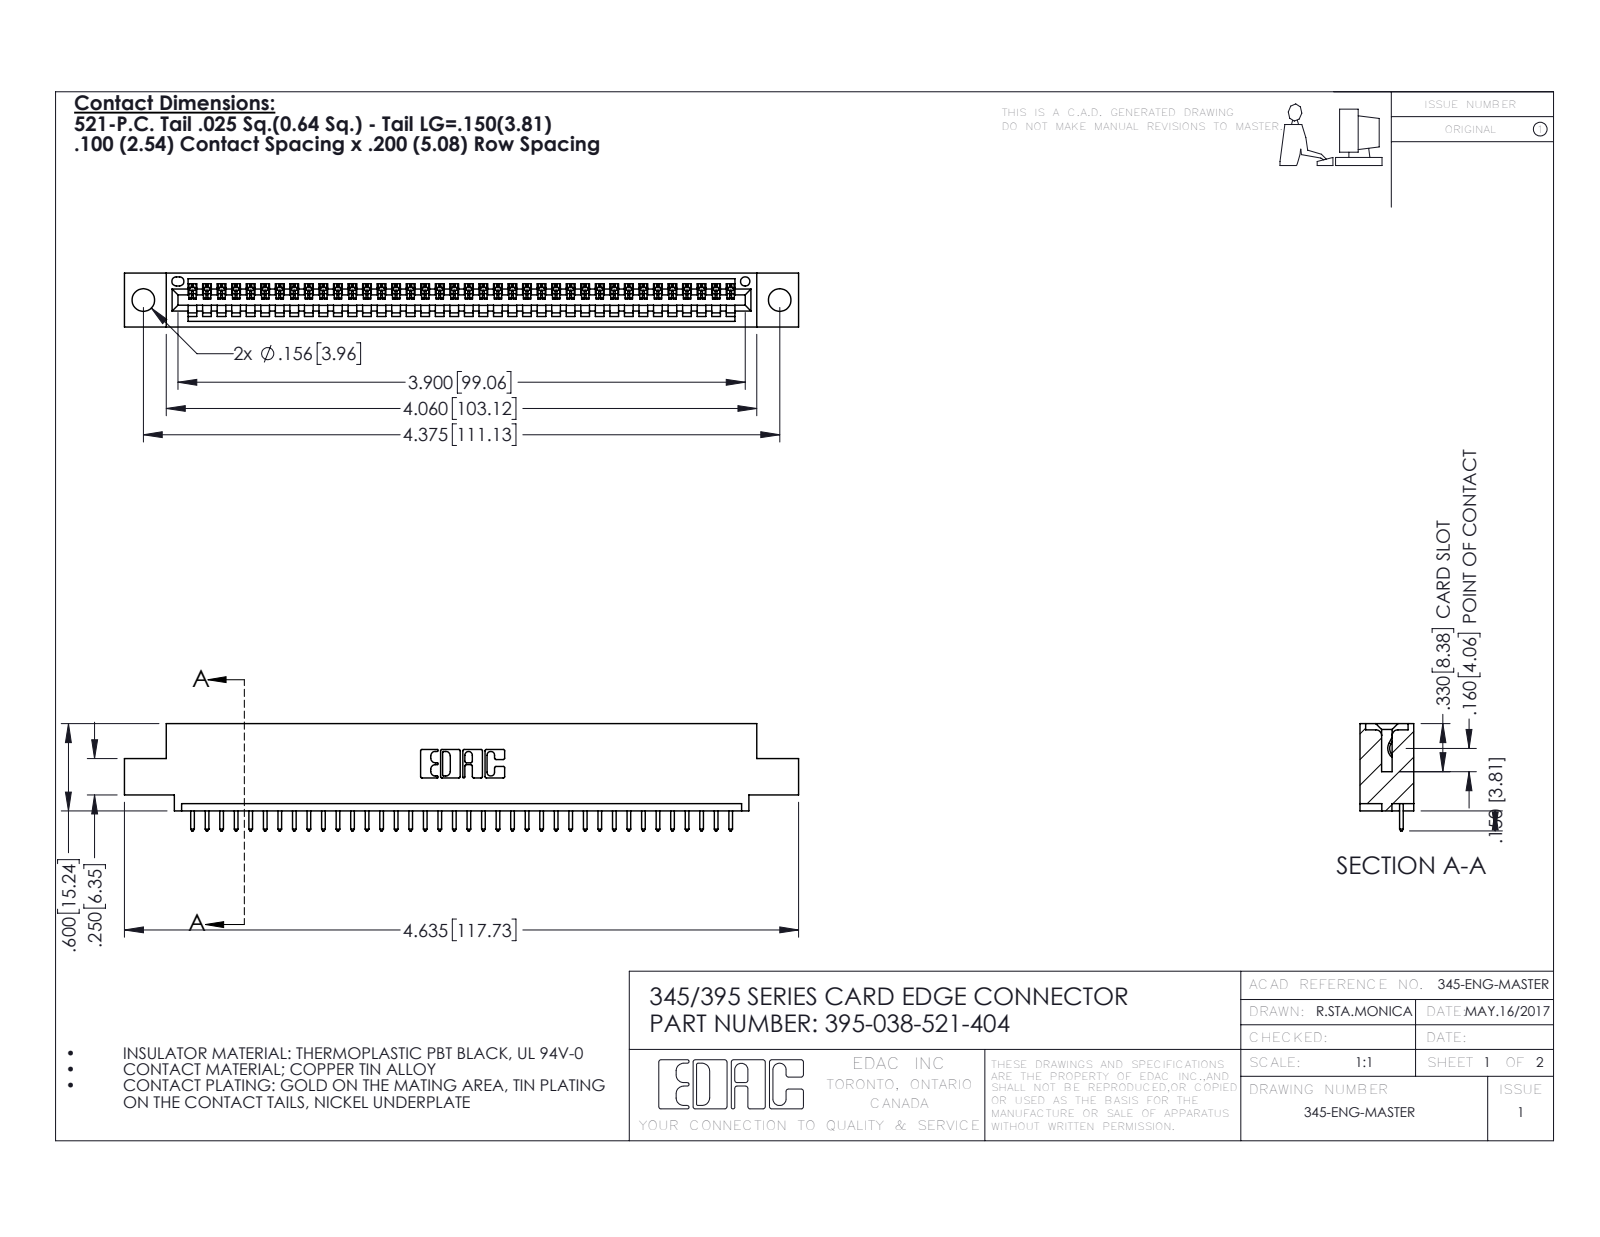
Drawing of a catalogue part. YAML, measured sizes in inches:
part_name: "395-038-521-404; 345 Part_0.110 Offset - 0.156 Dia-TH; 345-292-001_345-293-121"
step_written_by: "SolidWorks 2016 (CONFIG_CONTROL_DESIGN)"
units: inches
bodies: {solids: 39, faces: 2334, planar: 1604, cylindrical: 730, other: 0}
overall_size: [4.635, 0.737, 0.37]
volume: 0.664
surface_area: 21.5
round_holes:
  - {diameter: 0.156, count: 2}
  - {diameter: 0.064, count: 1}
partial_cylinders:
  - {radius: 0.006, count: 76}
  - {radius: 0.01, count: 76}
  - {radius: 0.01, count: 22}
  - {radius: 0.007, count: 6}
  - {radius: 0.031, count: 6}
  - {radius: 0.026, count: 3}
  - {radius: 0.031, count: 2}
  - {radius: 0.04, count: 2}
face_to_face_distances: [0.298, 0.072, 0.37, 0.2, 0.098, 0.272, 0.025, 0.225, 0.149, 0.072]
hole_center_spacings: [0.27, 4.139, 4.375]
